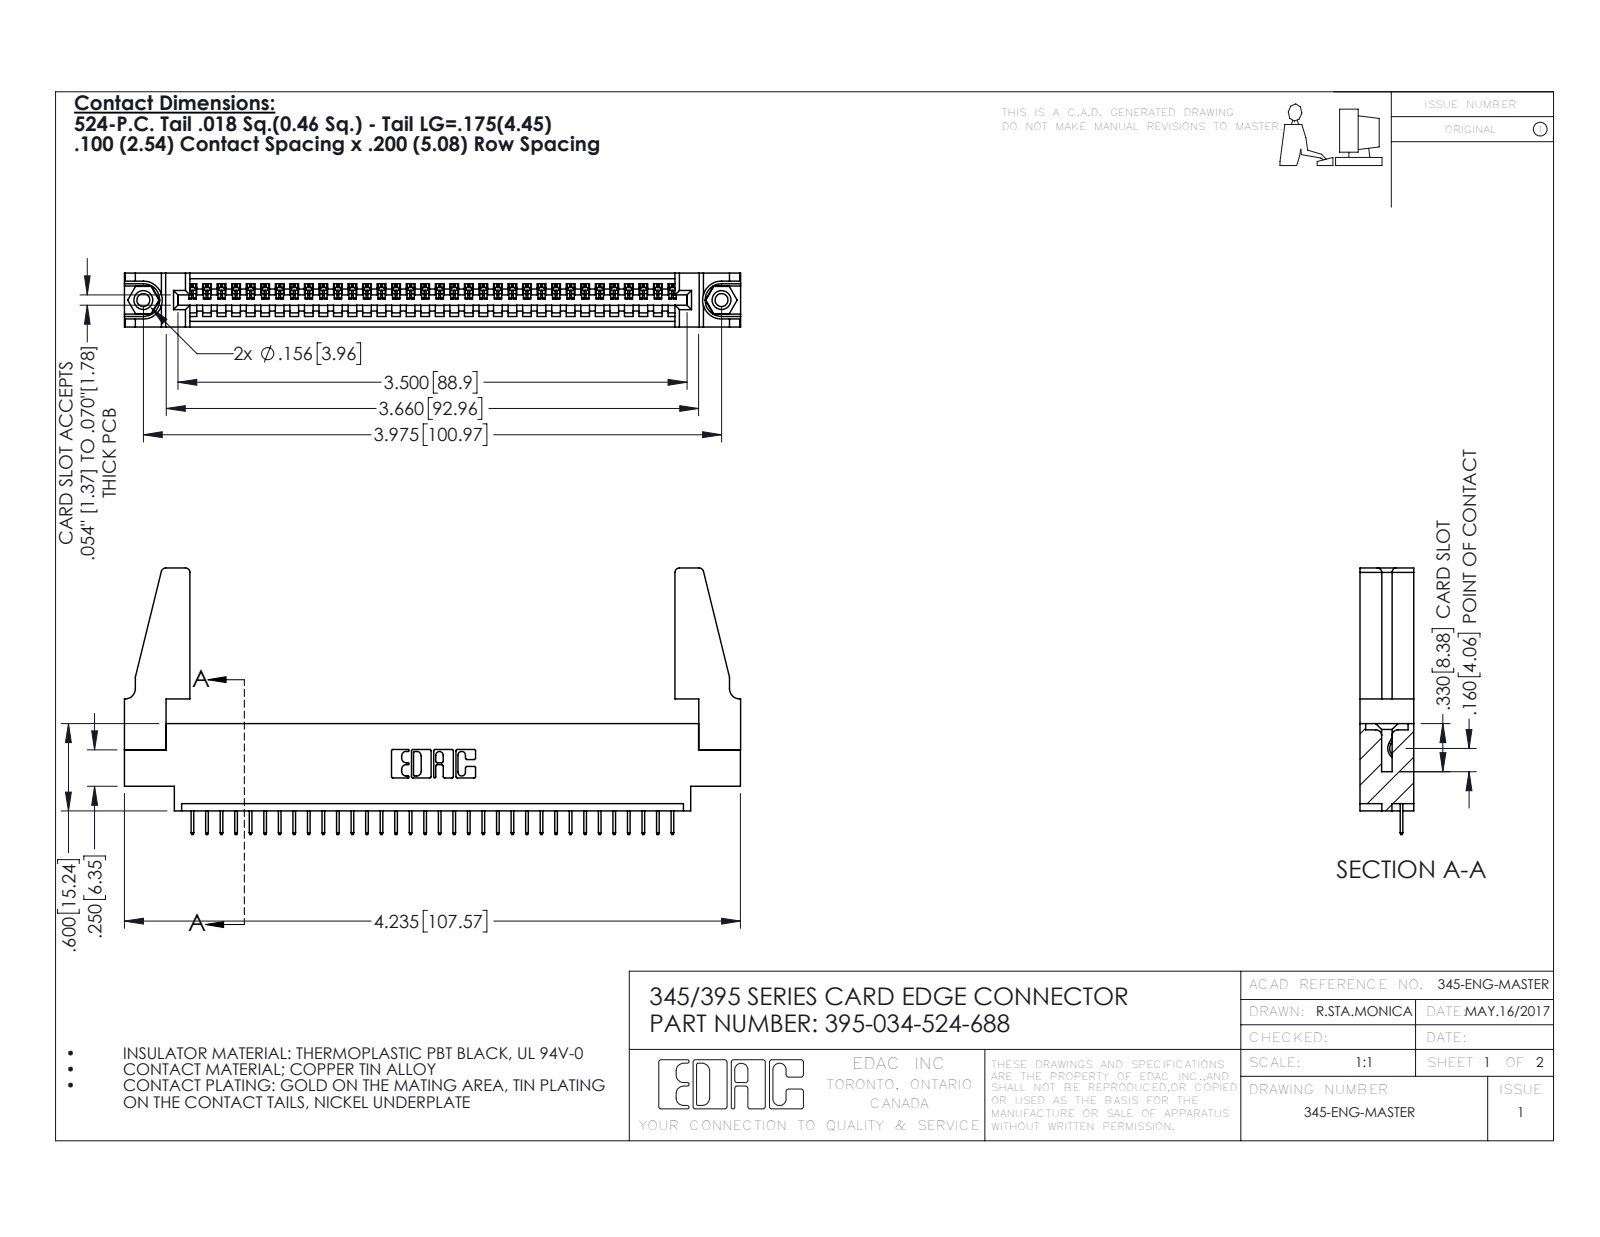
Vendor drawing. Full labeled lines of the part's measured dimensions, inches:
Part name (STEP PRODUCT): 395-034-524-688; 345-220-078_345-220-088; 345-250-001_345-250-001-102; 345-292-001_345-293-124 (+1 more)
STEP written by: SolidWorks 2016 (CONFIG_CONTROL_DESIGN)
Units: inches
Bodies: 39 solids, 2362 faces (1720 planar, 626 cylindrical, 16 other)
Overall size (bounding box): 4.236 × 1.832 × 0.37
Volume: 0.803 in³ · Surface area: 24.62 in²
Round holes (diameter × count): ⌀0.089 ×2, ⌀0.125 ×2, ⌀0.156 ×2, ⌀0.064 ×1
Round bosses / shafts (diameter × count): ⌀0.155 ×2
Partial cylindrical surfaces — rounded edges, fillets, slot ends (radius × count): R0.006 ×68, R0.01 ×22, R0.03 ×8, R0.007 ×6, R0.031 ×6, R0.026 ×3, R0.031 ×2, R0.04 ×2
Main face-to-face distances: 0.37, 0.072, 0.298, 0.2, 0.098, 0.272, 0.025, 0.225, 0.072, 0.175
Hole centre spacings: 0.27, 3.74, 3.975
